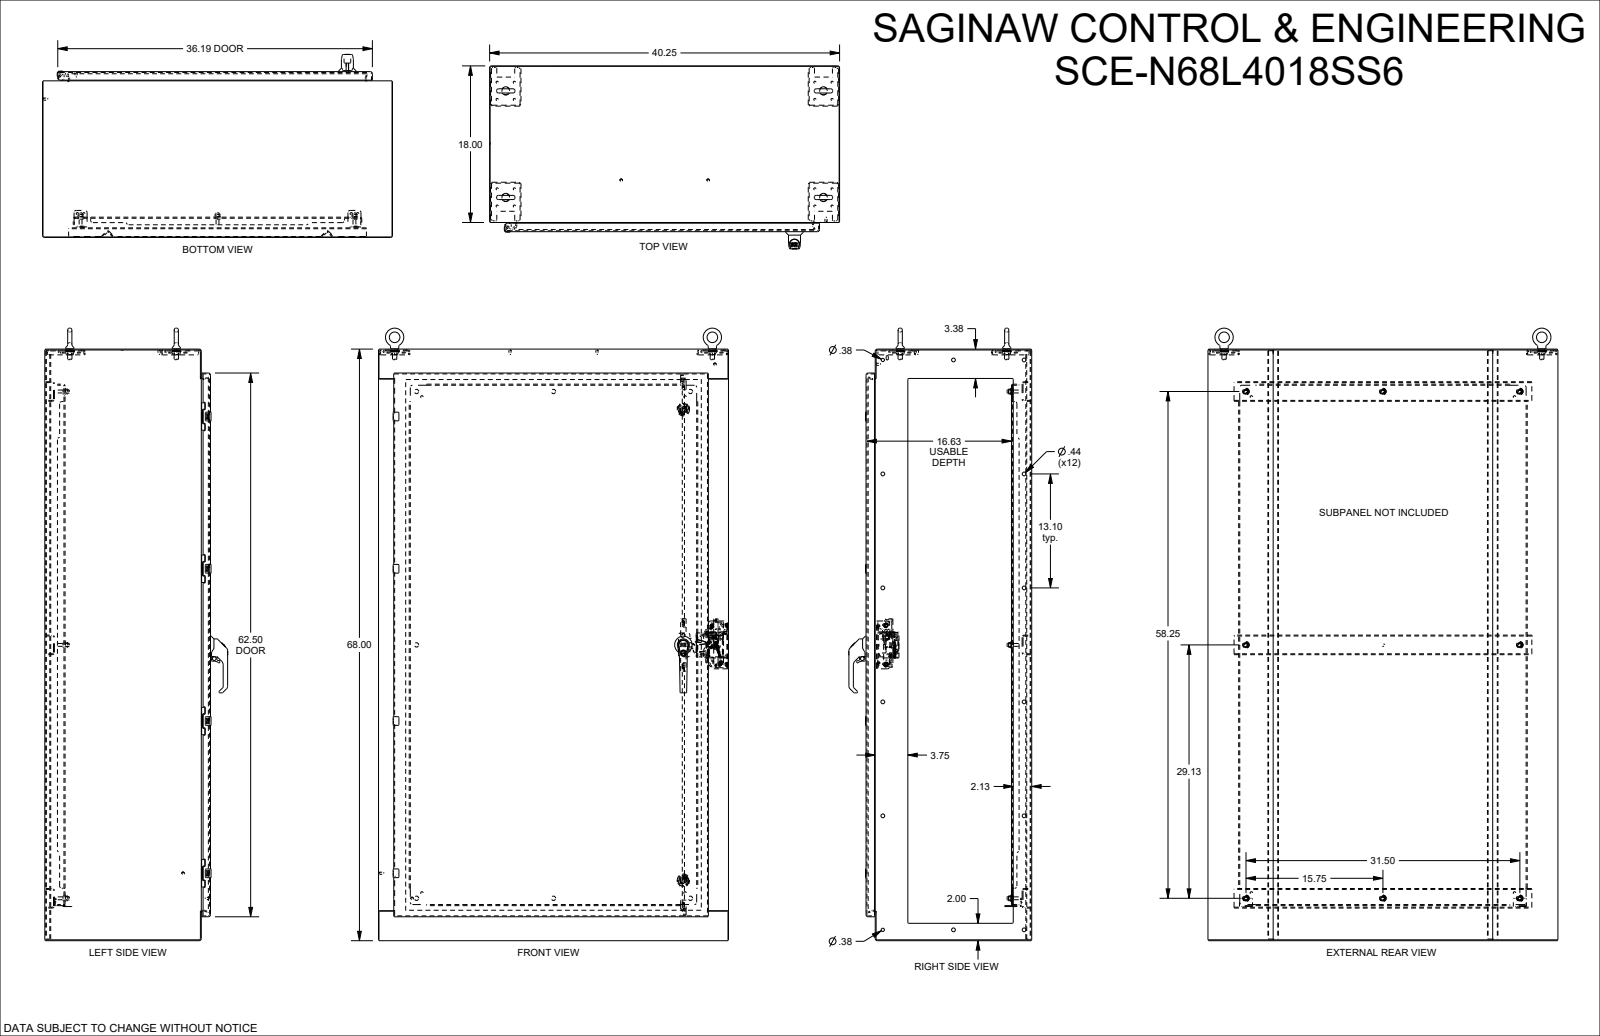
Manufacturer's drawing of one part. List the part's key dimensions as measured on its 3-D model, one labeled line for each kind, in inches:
Part name (STEP PRODUCT): SCE-N68L4018
STEP written by: SolidWorks 2023 (AUTOMOTIVE_DESIGN)
Units: inches
Bodies: 31 solids, 5241 faces (1988 planar, 1712 cylindrical, 1541 other)
Overall size (bounding box): 70.945 × 40.25 × 21.046
Volume: 1 049 in³ · Surface area: 19 758 in²
Round holes (diameter × count): ⌀0.25 ×18, ⌀0.437 ×12, ⌀0.375 ×10, ⌀0.205 ×8, ⌀0.244 ×8, ⌀0.04 ×4, ⌀0.17 ×4, ⌀0.218 ×4, ⌀0.256 ×4, ⌀0.875 ×4, ⌀0.135 ×2, ⌀0.156 ×2
Round bosses / shafts (diameter × count): ⌀0.17 ×12, ⌀0.25 ×11, ⌀0.24 ×8, ⌀0.196 ×5, ⌀1.173 ×4, ⌀0.6 ×4, ⌀1.4 ×2, ⌀0.48 ×2
Partial cylindrical surfaces — rounded edges, fillets, slot ends (radius × count): R0.015 ×234, R0.03 ×130, R0.125 ×87, R0.062 ×52, R0.167 ×38, R0.02 ×37, R0.229 ×32, R0.25 ×31
Main face-to-face distances: 0.104, 18.954, 19.058, 18.85, 0.104, 67.896, 17.896, 1.058, 40.146, 67.792
Hole centre spacings: 1.979, 1.4, 17.5, 13.1, 20.873, 2.799, 11.304, 12.25
